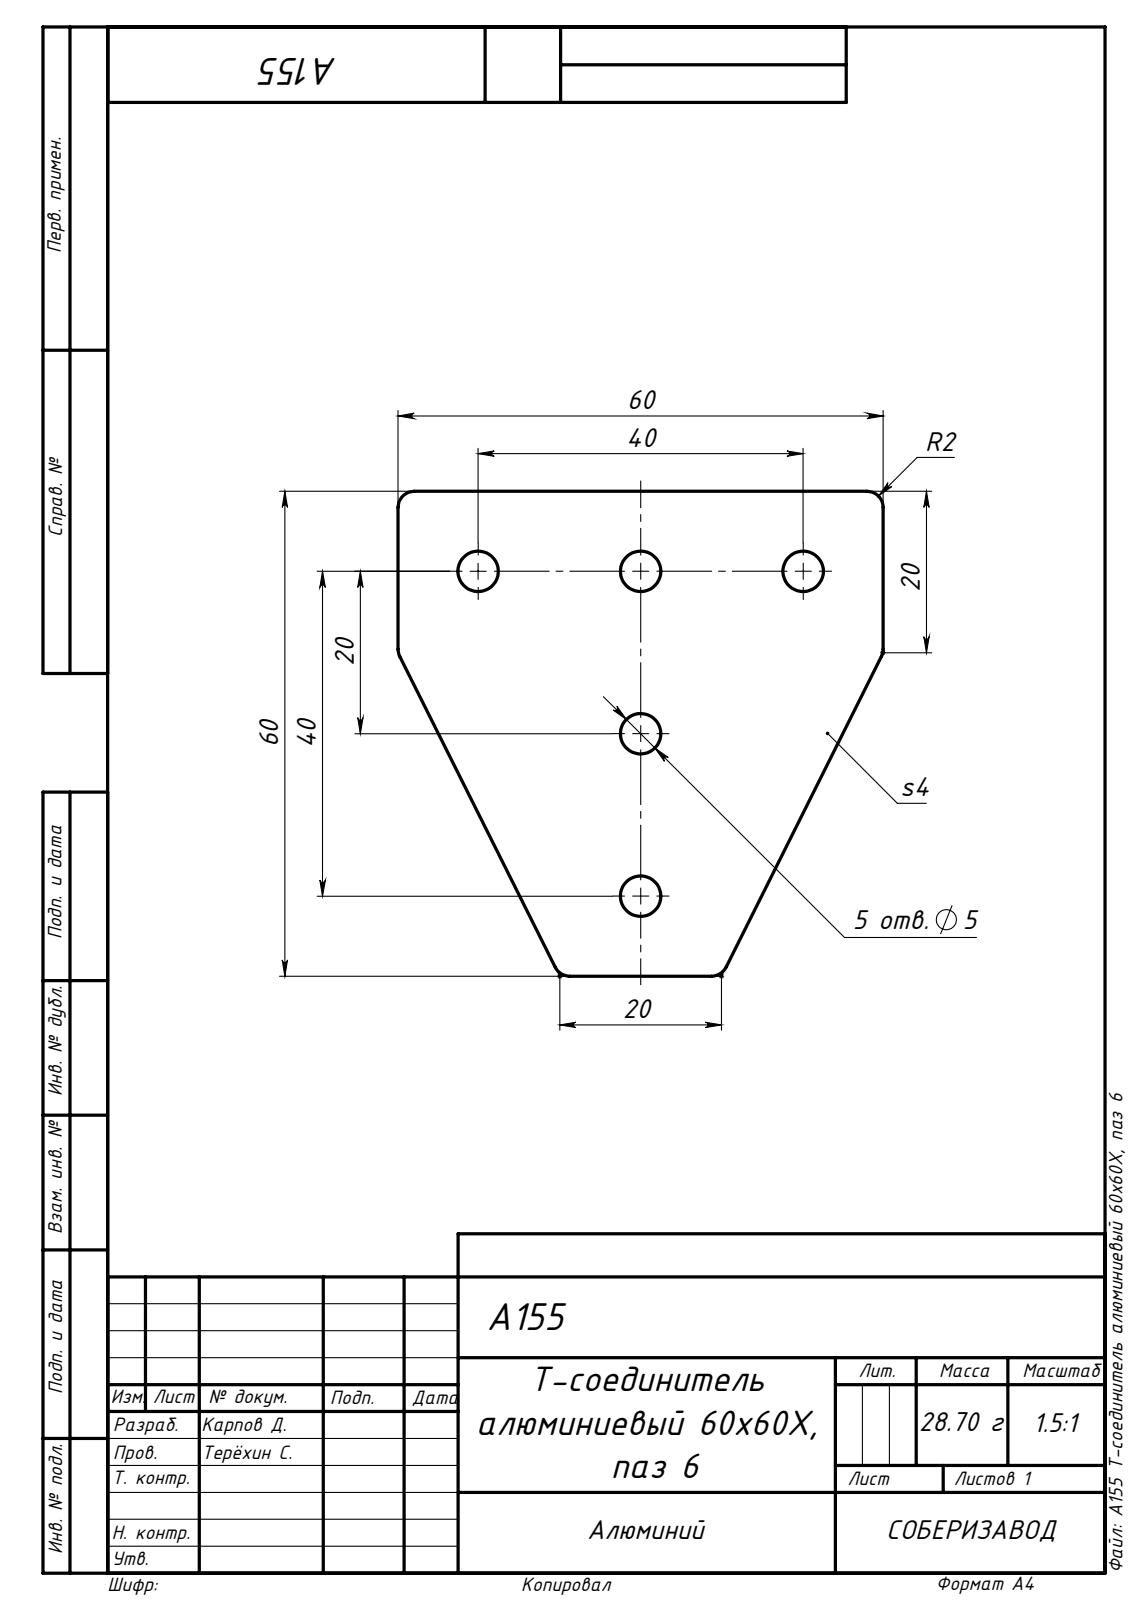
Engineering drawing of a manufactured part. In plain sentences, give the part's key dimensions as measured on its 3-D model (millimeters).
Its 3-D file was written by "SolidWorks 2019 (AUTOMOTIVE_DESIGN)". It is 1 solid with 24 faces: 8 planar, 16 cylindrical and 0 other. Overall it measures 60 by 54.64 by 4 millimeters. Its volume is 9 941 cubic millimeters and its surface area 6 076 square millimeters. Round holes: 5 of diameter 5. Partial cylindrical surfaces (rounded edges, fillets, slot ends): 6 of radius 2. The main face-to-face distances are 4, 54.64, 60. The hole center spacings are 20.5, 25.78, 41.12, 15.64, 20, 35.64, 41.
